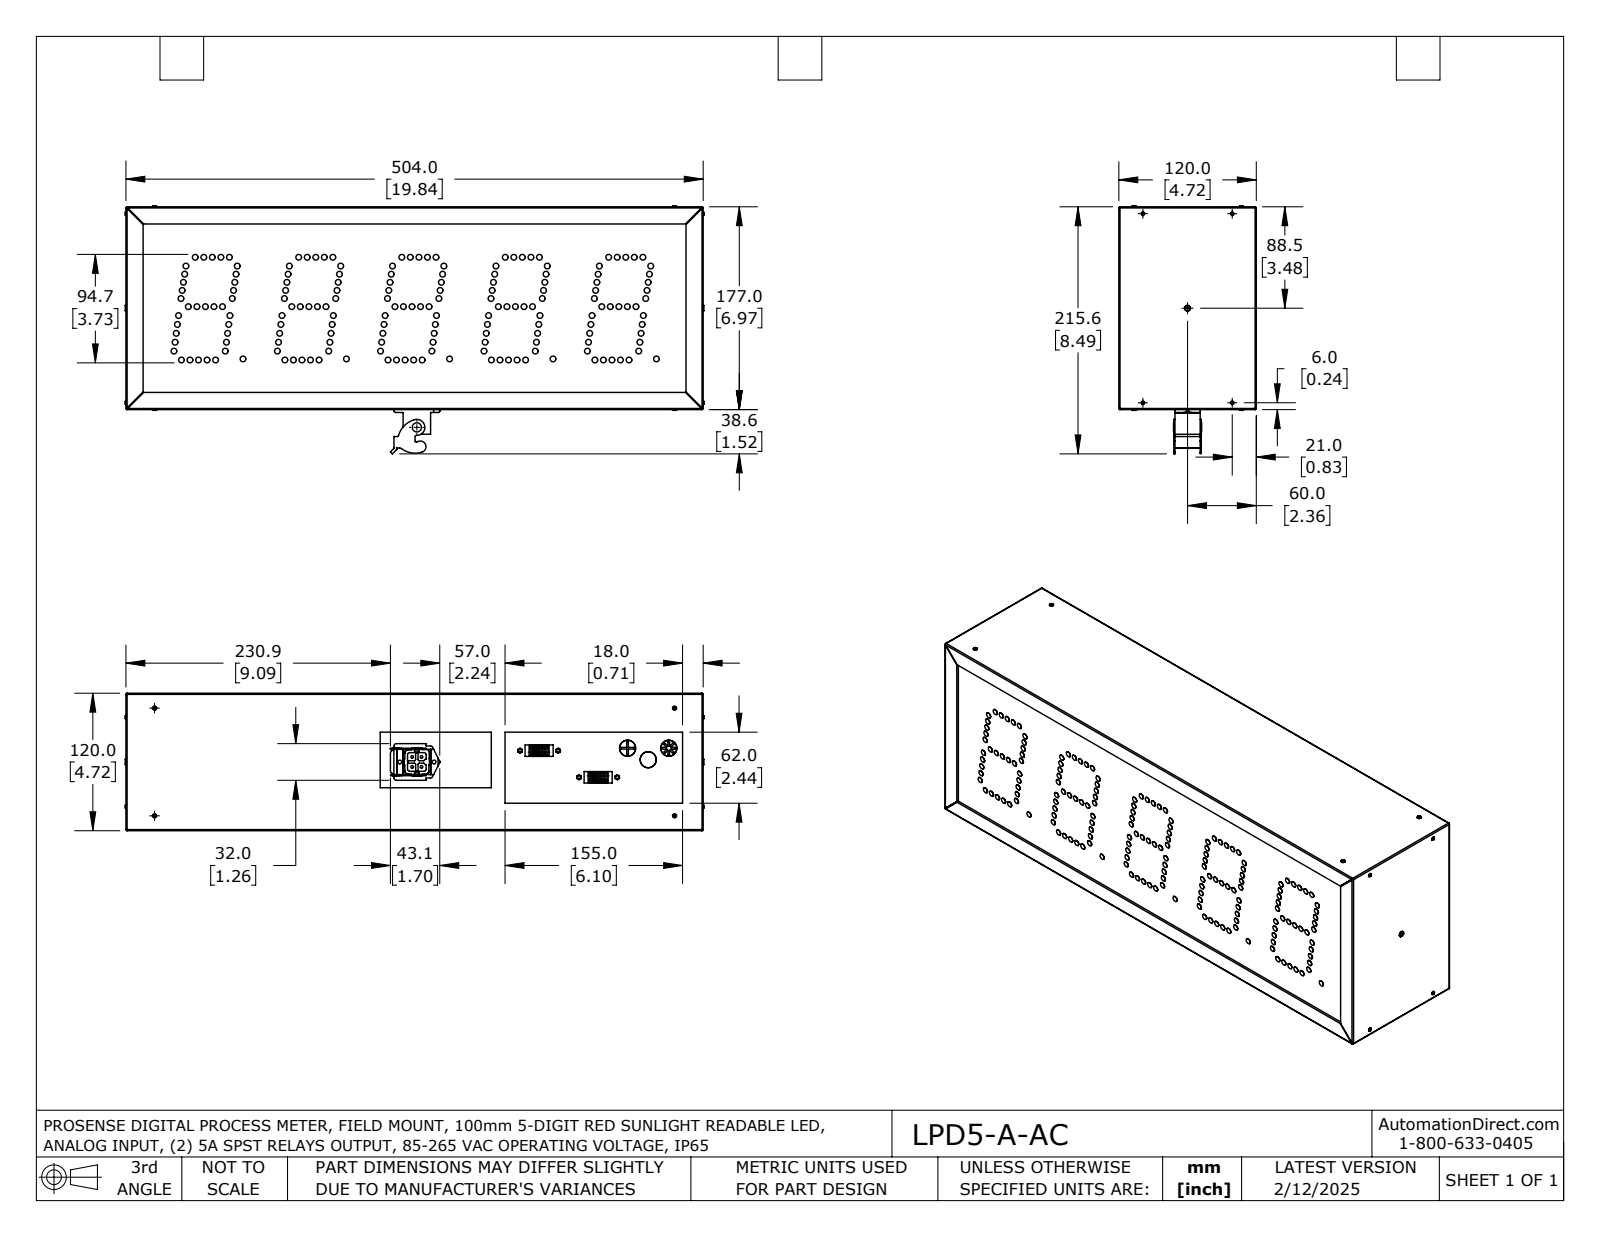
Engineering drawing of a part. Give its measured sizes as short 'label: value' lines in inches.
name: LPD5-A-AC
written by: SolidWorks 2021 (AUTOMOTIVE_DESIGN)
unit: in
bodies: 4 solids, 1918 faces (1232 planar, 640 cylindrical, 46 other)
size: 19.894 × 8.515 × 4.724
volume: 644.2 in³; area: 546.4 in²
holes: 4× ⌀0.091, 4× ⌀0.098, 4× ⌀0.1, 3× ⌀0.553, 2× ⌀0.13, 1× ⌀0.059, 1× ⌀0.203, 1× ⌀0.315
bosses: 180× ⌀0.197, 12× ⌀0.031, 4× ⌀0.138, 4× ⌀0.118, 3× ⌀0.551, 1× ⌀0.187
rounds: 19× R0.039, 7× R0.079, 6× R0.035, 4× R0.046, 4× R0.069, 3× R0.042, 3× R0.042, 3× R0.098
face distances: 4.646, 6.969, 19.843, 0.079, 4.724, 0.059, 6.909, 4.648, 0.077, 0.591
hole spacings: 3.593, 0.32, 0.343, 0.469, 0.811, 1.311, 2.226, 3.071
